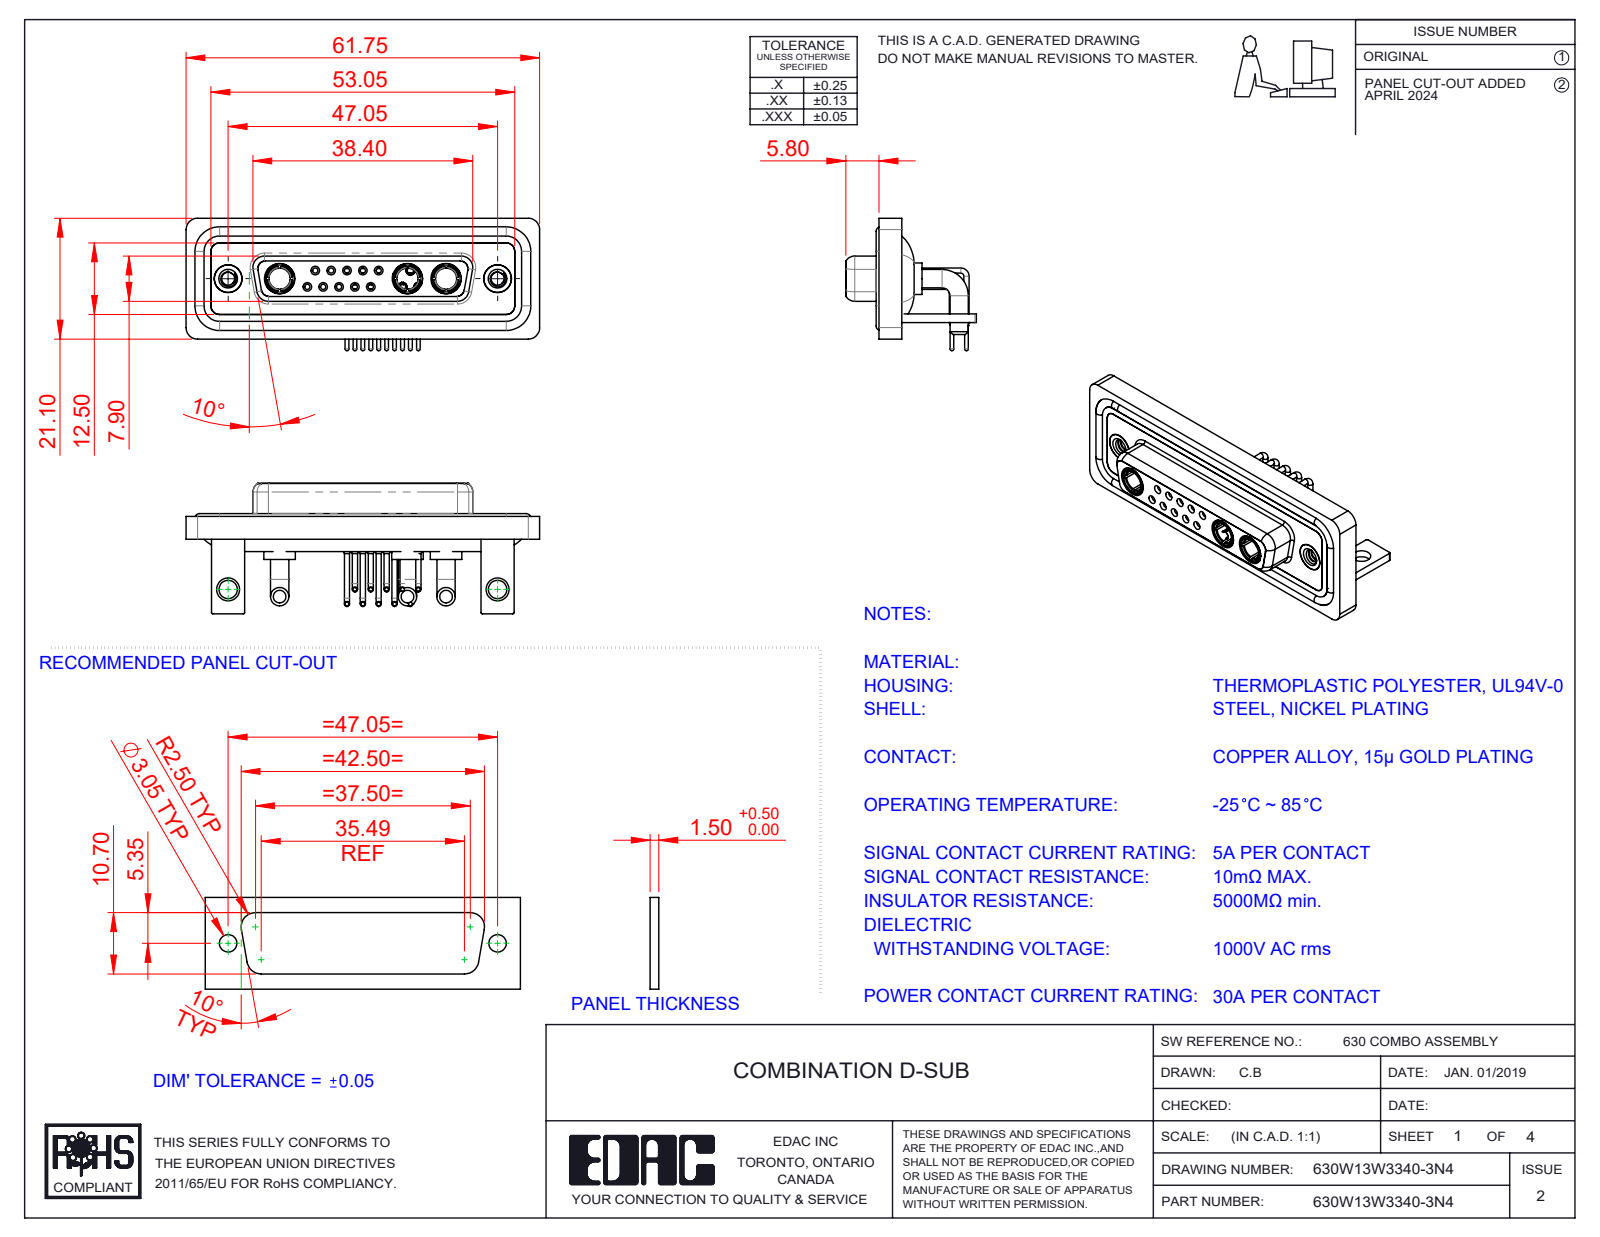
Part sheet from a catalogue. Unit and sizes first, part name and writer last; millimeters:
Units: millimetres
Overall size (bounding box): 61.75 × 23.12 × 22.8
Round holes (diameter × count): ⌀0.9 ×10, ⌀1.1 ×10, ⌀1.5 ×10, ⌀2 ×10, ⌀1.6 ×5, ⌀1.7 ×5, ⌀4.85 ×5, ⌀3.7 ×3, ⌀5.3 ×3, ⌀2.26 ×2, ⌀3.2 ×2, ⌀4 ×2
Round bosses / shafts (diameter × count): ⌀0.9 ×15, ⌀1.6 ×12, ⌀0.65 ×10, ⌀3.2 ×6, ⌀2 ×5, ⌀1.5 ×5, ⌀5.5 ×3, ⌀5.2 ×3
Partial cylindrical surfaces — rounded edges, fillets, slot ends (radius × count): R2 ×19, R1.5 ×18, R0.25 ×16, R1.35 ×8, R1.6 ×8, R0.5 ×5, R0.6 ×4, R0.65 ×4
Main face-to-face distances: 0.4, 1.8, 2.9, 3.7, 1.5, 4.1, 1.1, 1.4, 1.6, 3.1
Hole centre spacings: 3.16, 2.77, 5.54, 5.04, 8.31, 5.03, 7.49, 11.08
Volume: 8 921 mm³ · Surface area: 15 087 mm²
Bodies: 25 solids, 1198 faces (362 planar, 517 cylindrical, 319 other)
Part name (STEP PRODUCT): 630Combo Contact Row 2_50 Contacts; 630Combo Housing_13W3; 630Combo Threaded Rivet_2; 630Combo Shell Front_25 Contacts (+6 more)
STEP written by: SolidWorks 2023 (CONFIG_CONTROL_DESIGN)
